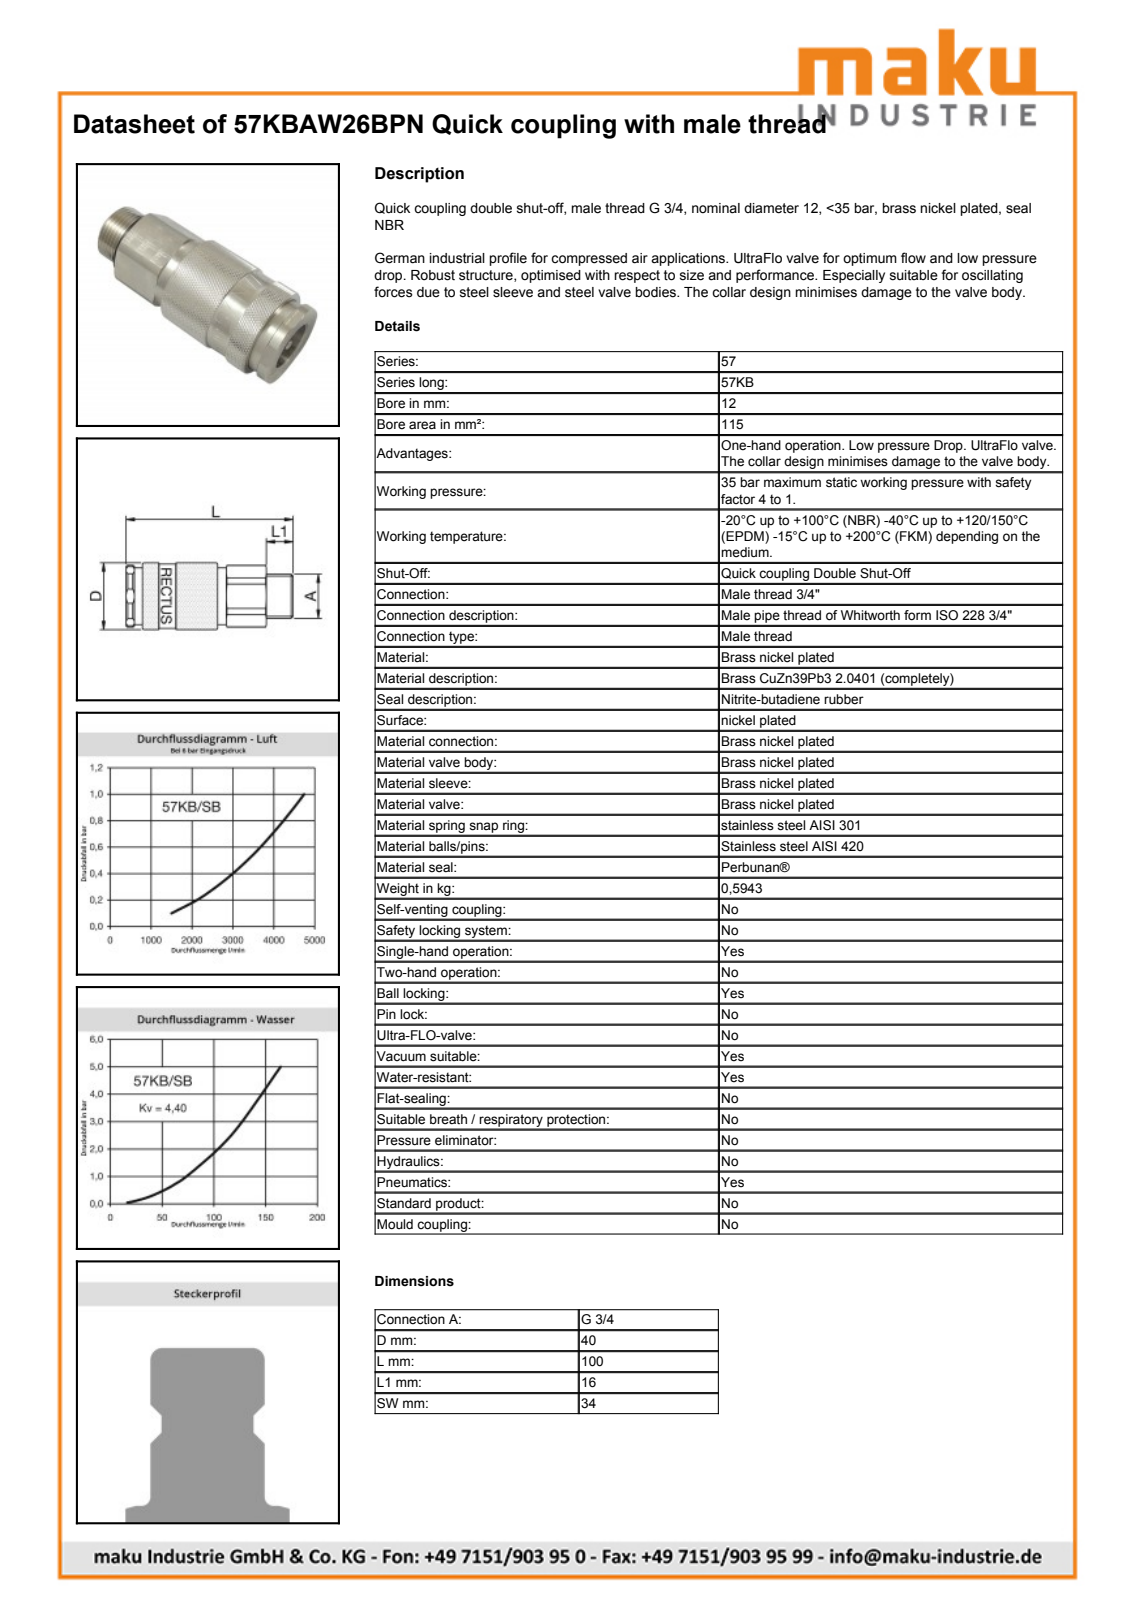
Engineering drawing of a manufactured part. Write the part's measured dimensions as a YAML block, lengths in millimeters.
part_name: "D107023"
step_written_by: "Autodesk Inventor 2013 (AUTOMOTIVE_DESIGN)"
units: millimeters
bodies: {solids: 2, faces: 516, planar: 204, cylindrical: 75, other: 237}
overall_size: [100.05, 40, 40]
volume: 98450
surface_area: 25194
round_holes:
  - {diameter: 28.95, count: 1}
  - {diameter: 30.2, count: 1}
  - {diameter: 34.2, count: 1}
  - {diameter: 34.6, count: 1}
round_bosses_or_shafts:
  - {diameter: 40, count: 1}
  - {diameter: 38.5, count: 1}
  - {diameter: 34, count: 1}
  - {diameter: 32, count: 1}
  - {diameter: 30, count: 1}
  - {diameter: 28.8, count: 1}
  - {diameter: 28.4, count: 1}
  - {diameter: 27.37, count: 1}
partial_cylinders:
  - {radius: 13.3, count: 1}
  - {radius: 18.5, count: 1}
  - {radius: 19.15, count: 1}
face_to_face_distances: [34.02, 100.05, 34, 16, 46.25, 86.05, 14, 37.8, 48.25, 62.25]
